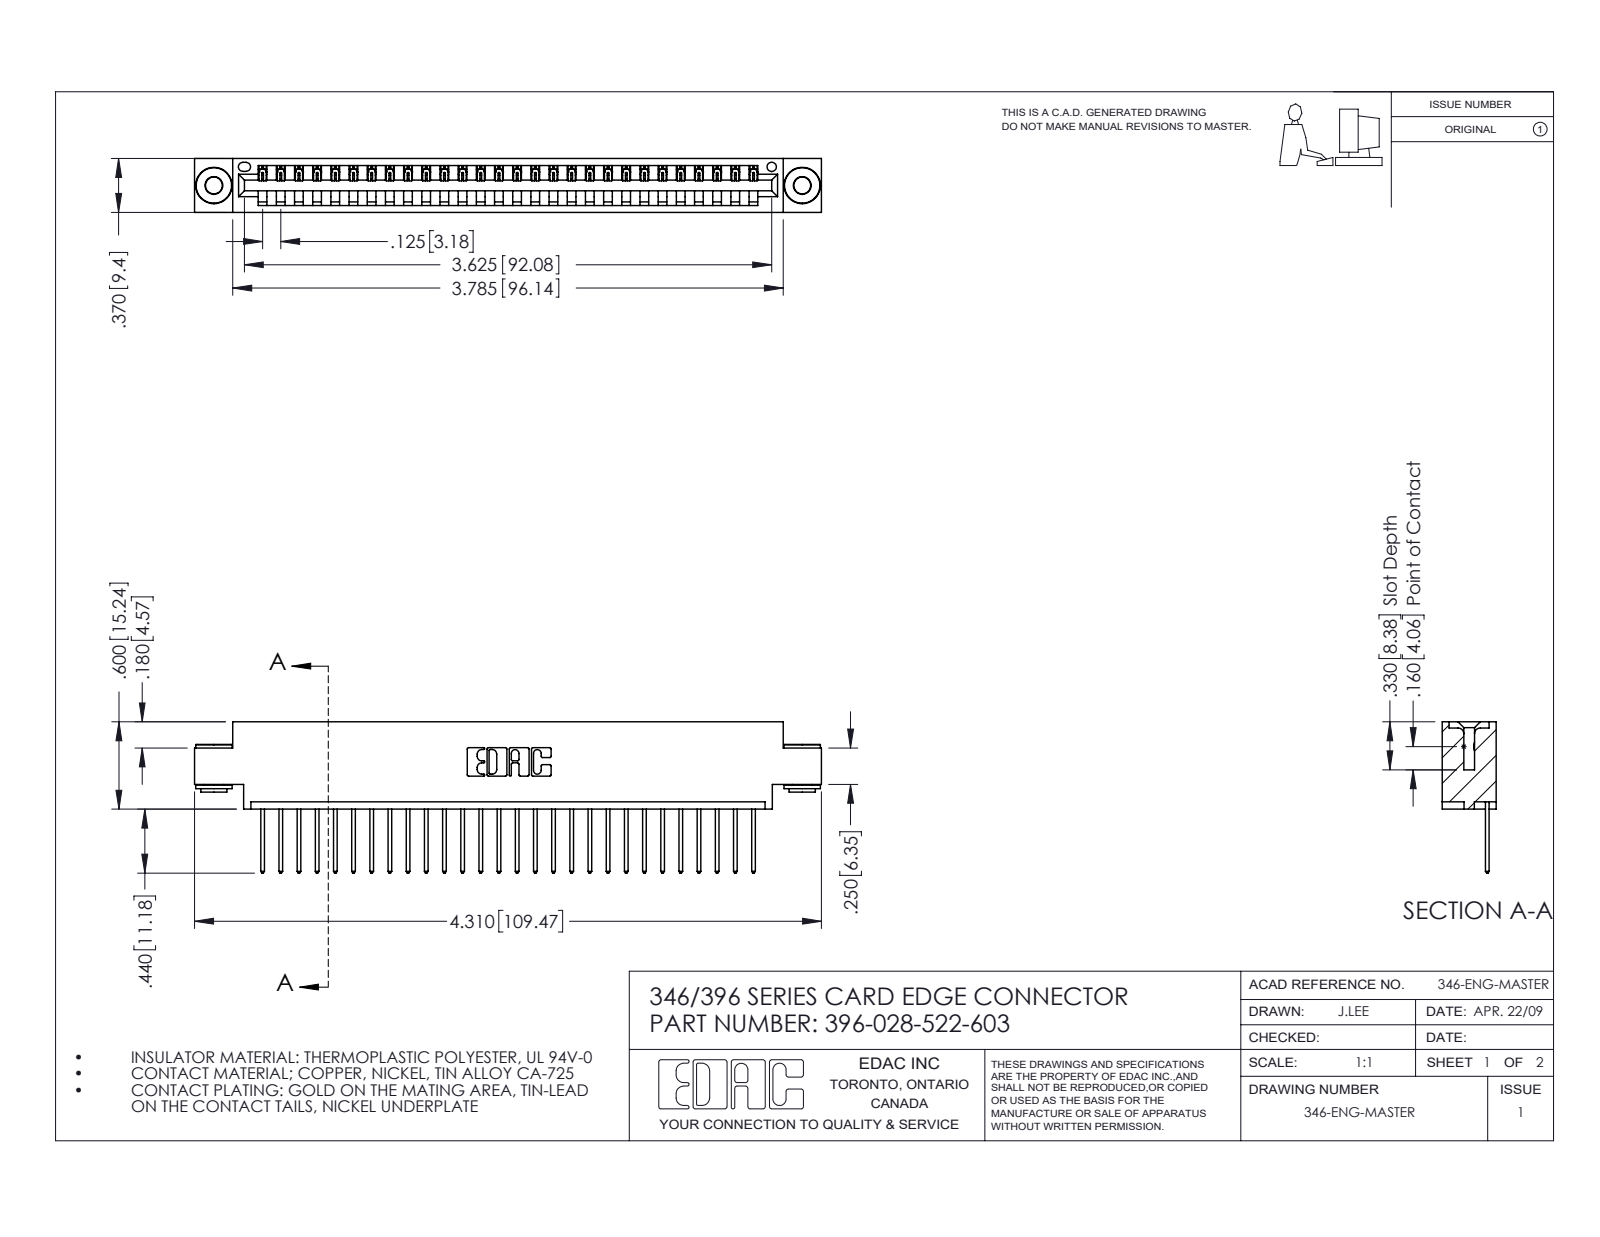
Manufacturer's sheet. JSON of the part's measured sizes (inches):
{"part_name": "346 Part_0.170 Offset - 0.156 Dia-TH; 345-250-002_345-250-002-102; 396-028-522-603; 345-292-001_345-293-122", "step_written_by": "SolidWorks 2016 (CONFIG_CONTROL_DESIGN)", "units": "inches", "bodies": {"solids": 31, "faces": 1788, "planar": 1210, "cylindrical": 570, "other": 8}, "overall_size": [4.31, 1.04, 0.37], "volume_in3": 0.626, "surface_area_in2": 20.37, "round_holes": [[0.116, 2], [0.156, 2], [0.064, 1]], "round_bosses_or_shafts": [[0.25, 2], [0.18, 2], [0.136, 2]], "partial_cylinders_radius": [[0.006, 56], [0.01, 56], [0.01, 22], [0.007, 6], [0.031, 6], [0.026, 3], [0.031, 2], [0.04, 2]], "face_to_face_distances": [0.048, 0.322, 0.37, 0.25, 0.025, 0.072, 0.298, 0.148, 0.222, 0.1], "hole_center_spacings": [0.246, 3.837, 4.045]}
